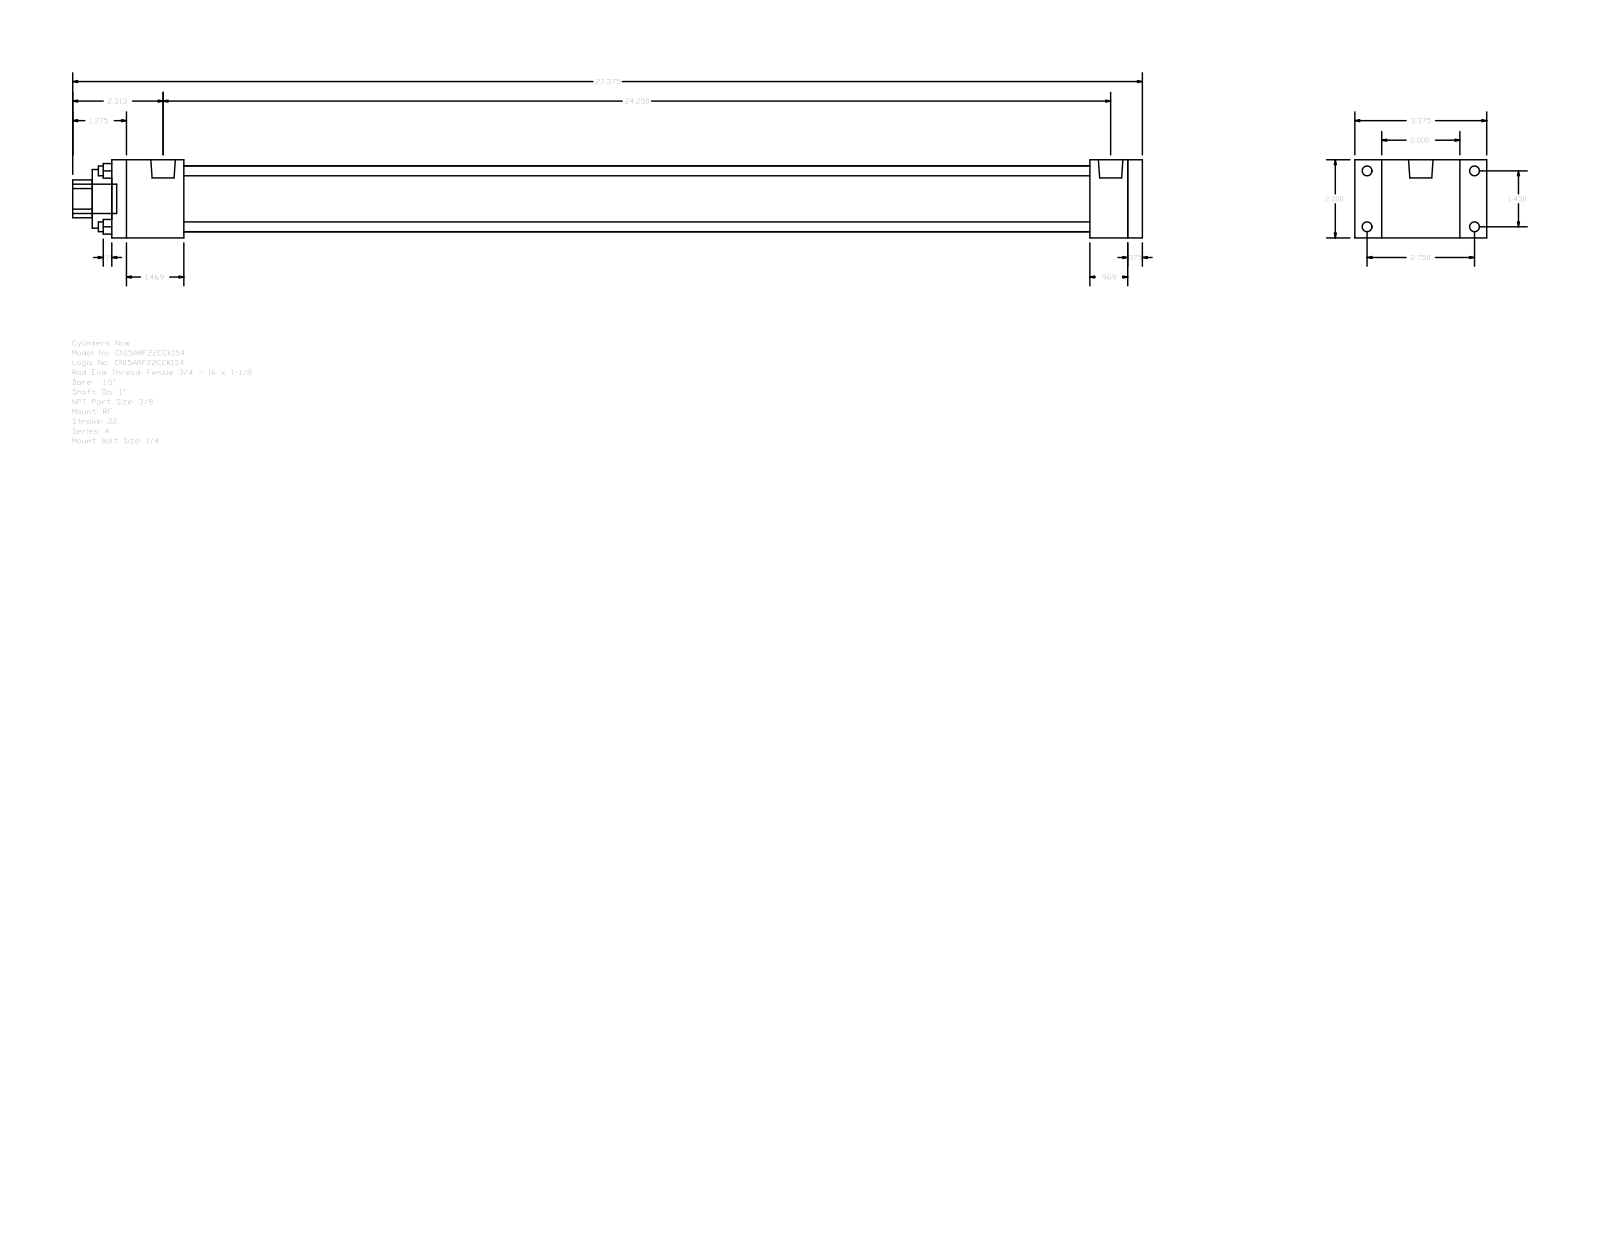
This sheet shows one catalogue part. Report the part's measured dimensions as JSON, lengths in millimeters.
{"part_name": "A_RF__0150_1", "step_written_by": "GSSL Pune (CONFIG_CONTROL_DESIGN)", "units": "millimeters", "bodies": {"solids": 0, "faces": 92, "planar": 64, "cylindrical": 28, "other": 0}, "overall_size": [695.33, 85.72, 50.8], "round_holes": [[6.35, 4], [25.4, 1], [38.1, 1], [42.93, 1]], "round_bosses_or_shafts": [[6.35, 4], [5.56, 4], [15.93, 2], [19.05, 1]], "partial_cylinders_radius": [[12.29, 1]], "face_to_face_distances": [50.8, 9.53, 660.4, 669.93, 635.79, 24.61, 34.14, 46.83, 588.96, 613.57], "hole_center_spacings": [25.68, 36.32, 51.36]}
